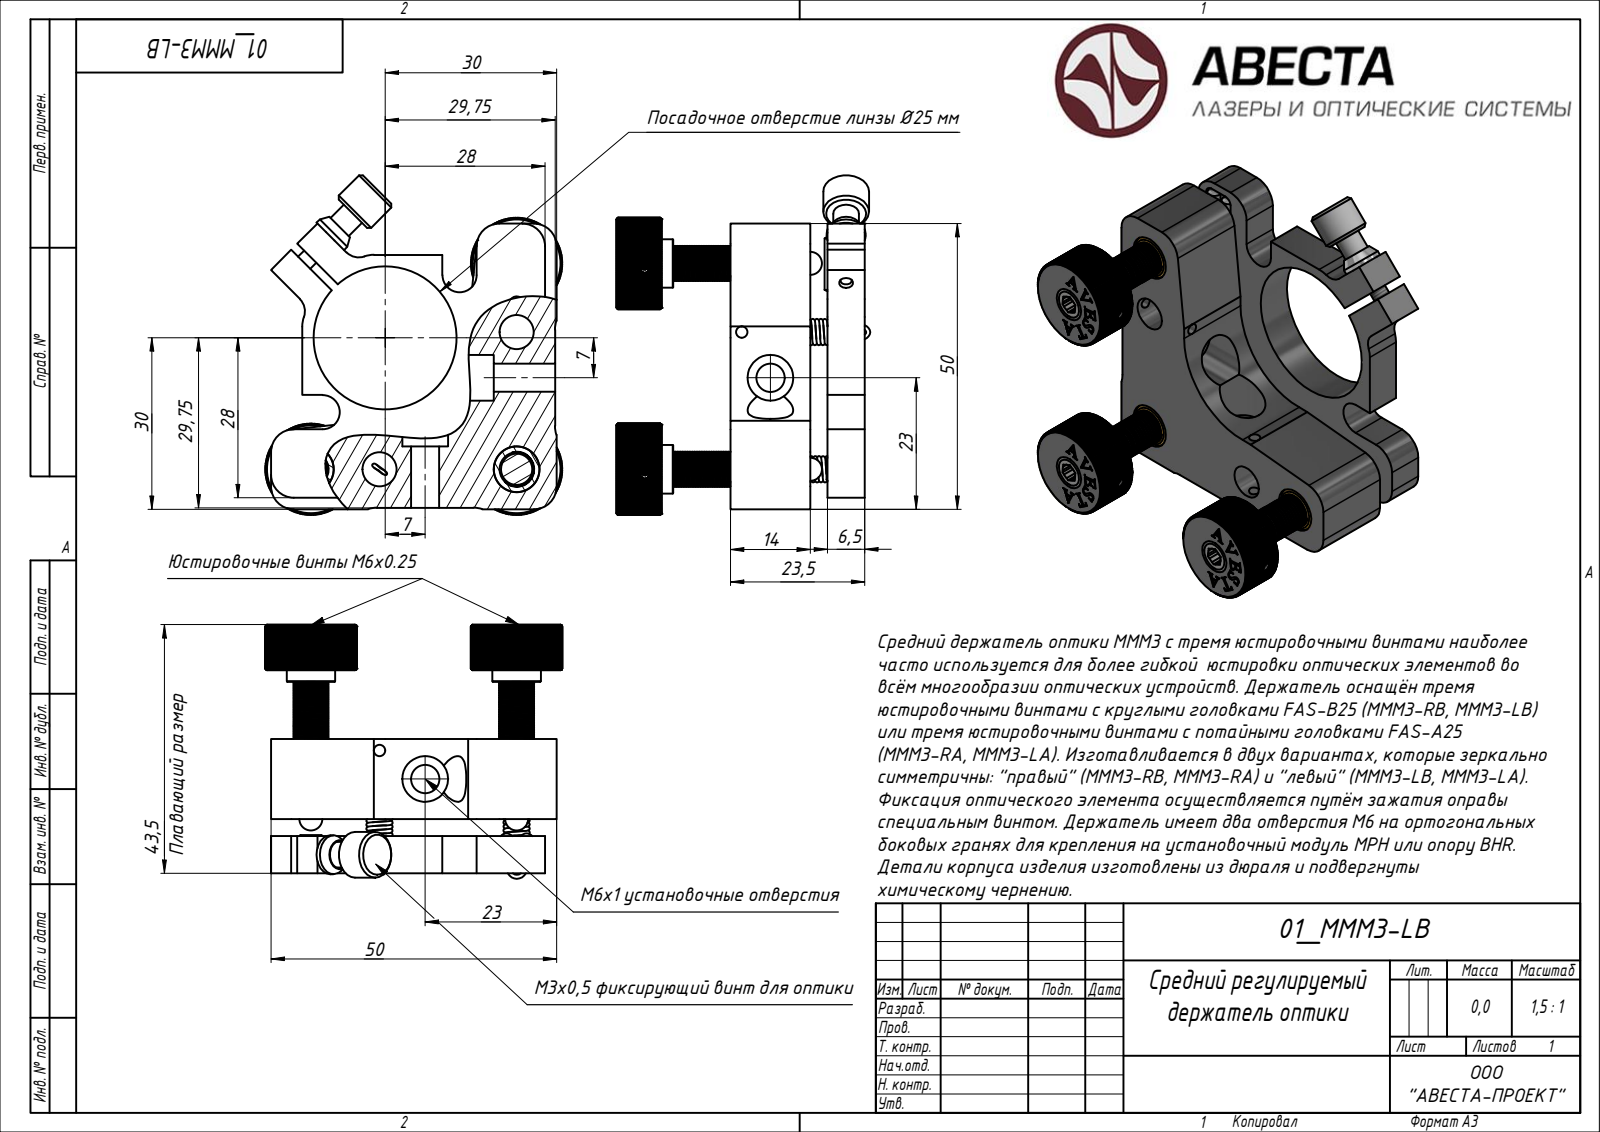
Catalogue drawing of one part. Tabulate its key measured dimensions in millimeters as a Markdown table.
| quantity | value |
| --- | --- |
| STEP written by | ST-DEVELOPER v15 (AUTOMOTIVE_DESIGN) |
| units | millimeters |
| bodies | 20 solids, 2816 faces (1555 planar, 0 cylindrical, 1261 other) |
| overall size | 59.41 × 52 × 44.25 |
| volume | 30 366 mm³ |
| surface area | 24 017 mm² |
| main face-to-face distances | 6.5, 3, 14, 9.5, 23.5, 17, 2, 12, 20, 7.7 |
